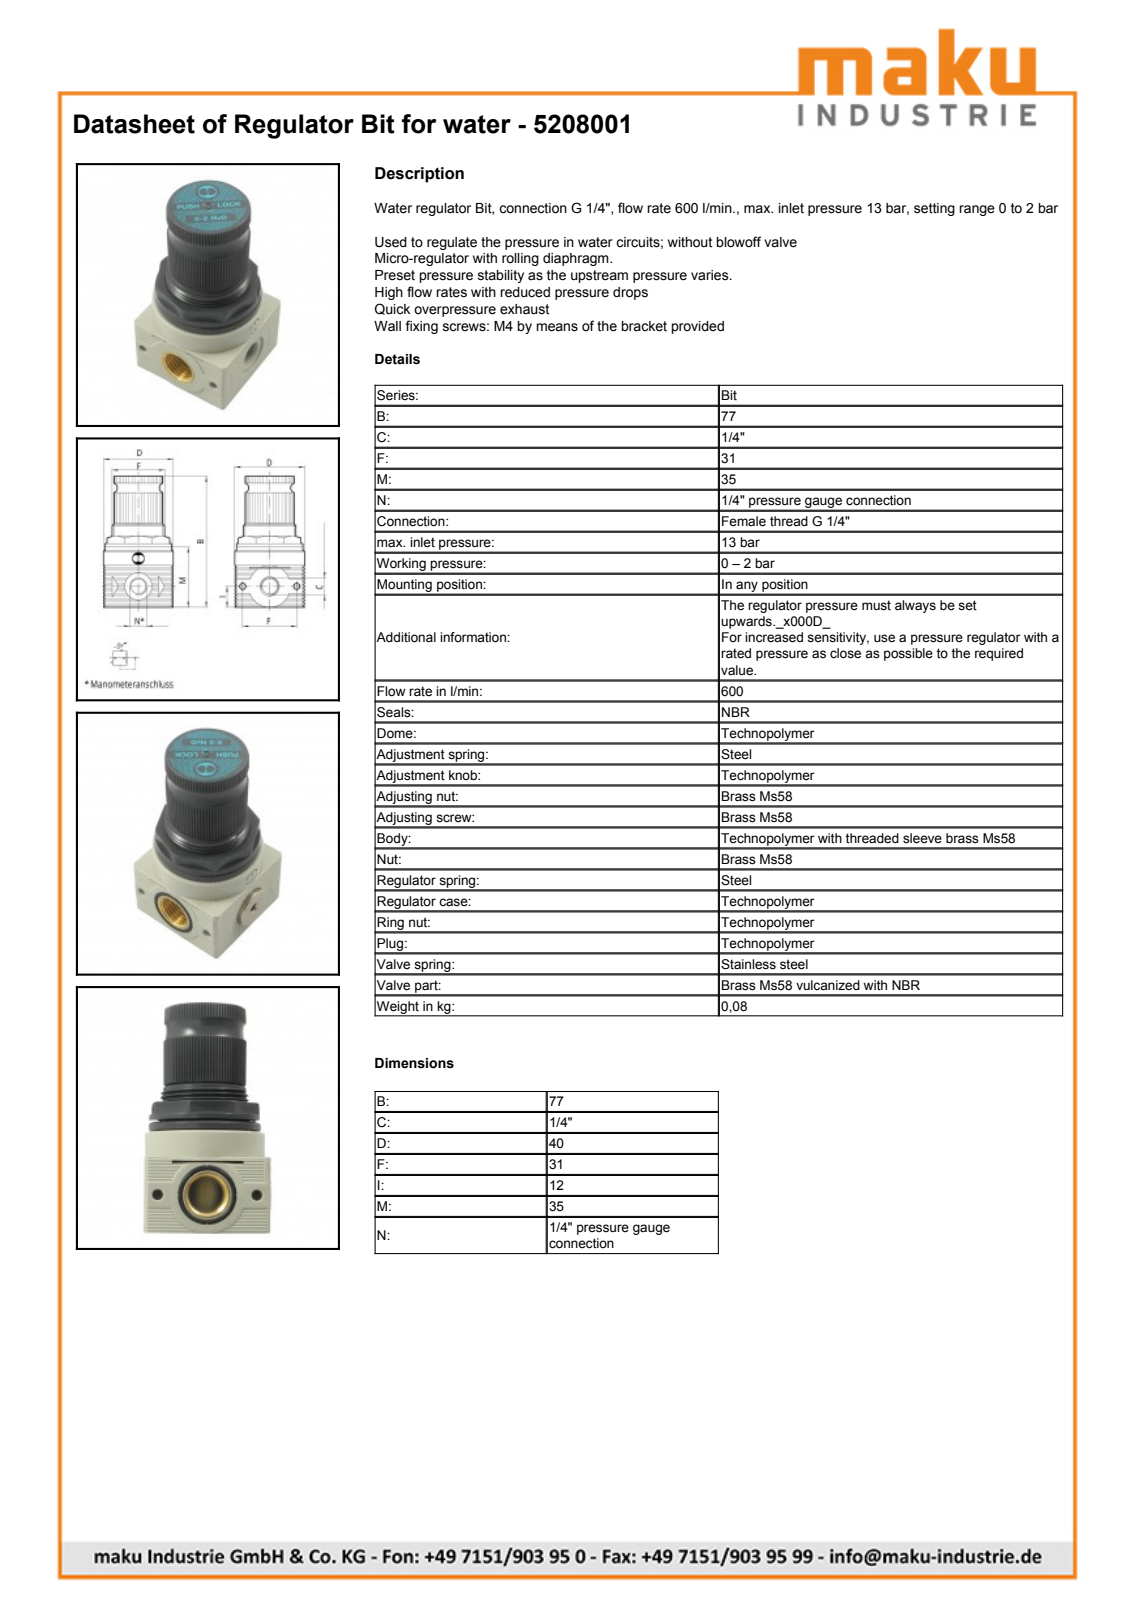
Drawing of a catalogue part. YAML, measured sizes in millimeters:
part_name: "5208001; 5208001-BD; 5208001-KN; 1/8-BIT"
step_written_by: "PARTsolutions (AUTOMOTIVE_DESIGN)"
units: millimeters
bodies: {solids: 3, faces: 127, planar: 92, cylindrical: 27, other: 8}
overall_size: [77, 41.5, 40]
volume: 76444
surface_area: 18319
round_holes:
  - {diameter: 4, count: 2}
  - {diameter: 8.57, count: 1}
  - {diameter: 11.45, count: 1}
  - {diameter: 15.5, count: 1}
round_bosses_or_shafts:
  - {diameter: 39.9, count: 1}
  - {diameter: 38, count: 1}
  - {diameter: 37.6, count: 1}
  - {diameter: 30, count: 1}
  - {diameter: 28, count: 1}
  - {diameter: 24, count: 1}
  - {diameter: 15, count: 1}
  - {diameter: 9.73, count: 1}
partial_cylinders:
  - {radius: 12, count: 1}
face_to_face_distances: [32, 40, 1, 9, 10, 39.95, 77, 45, 39, 19]
hole_center_spacings: [15.5, 31]
